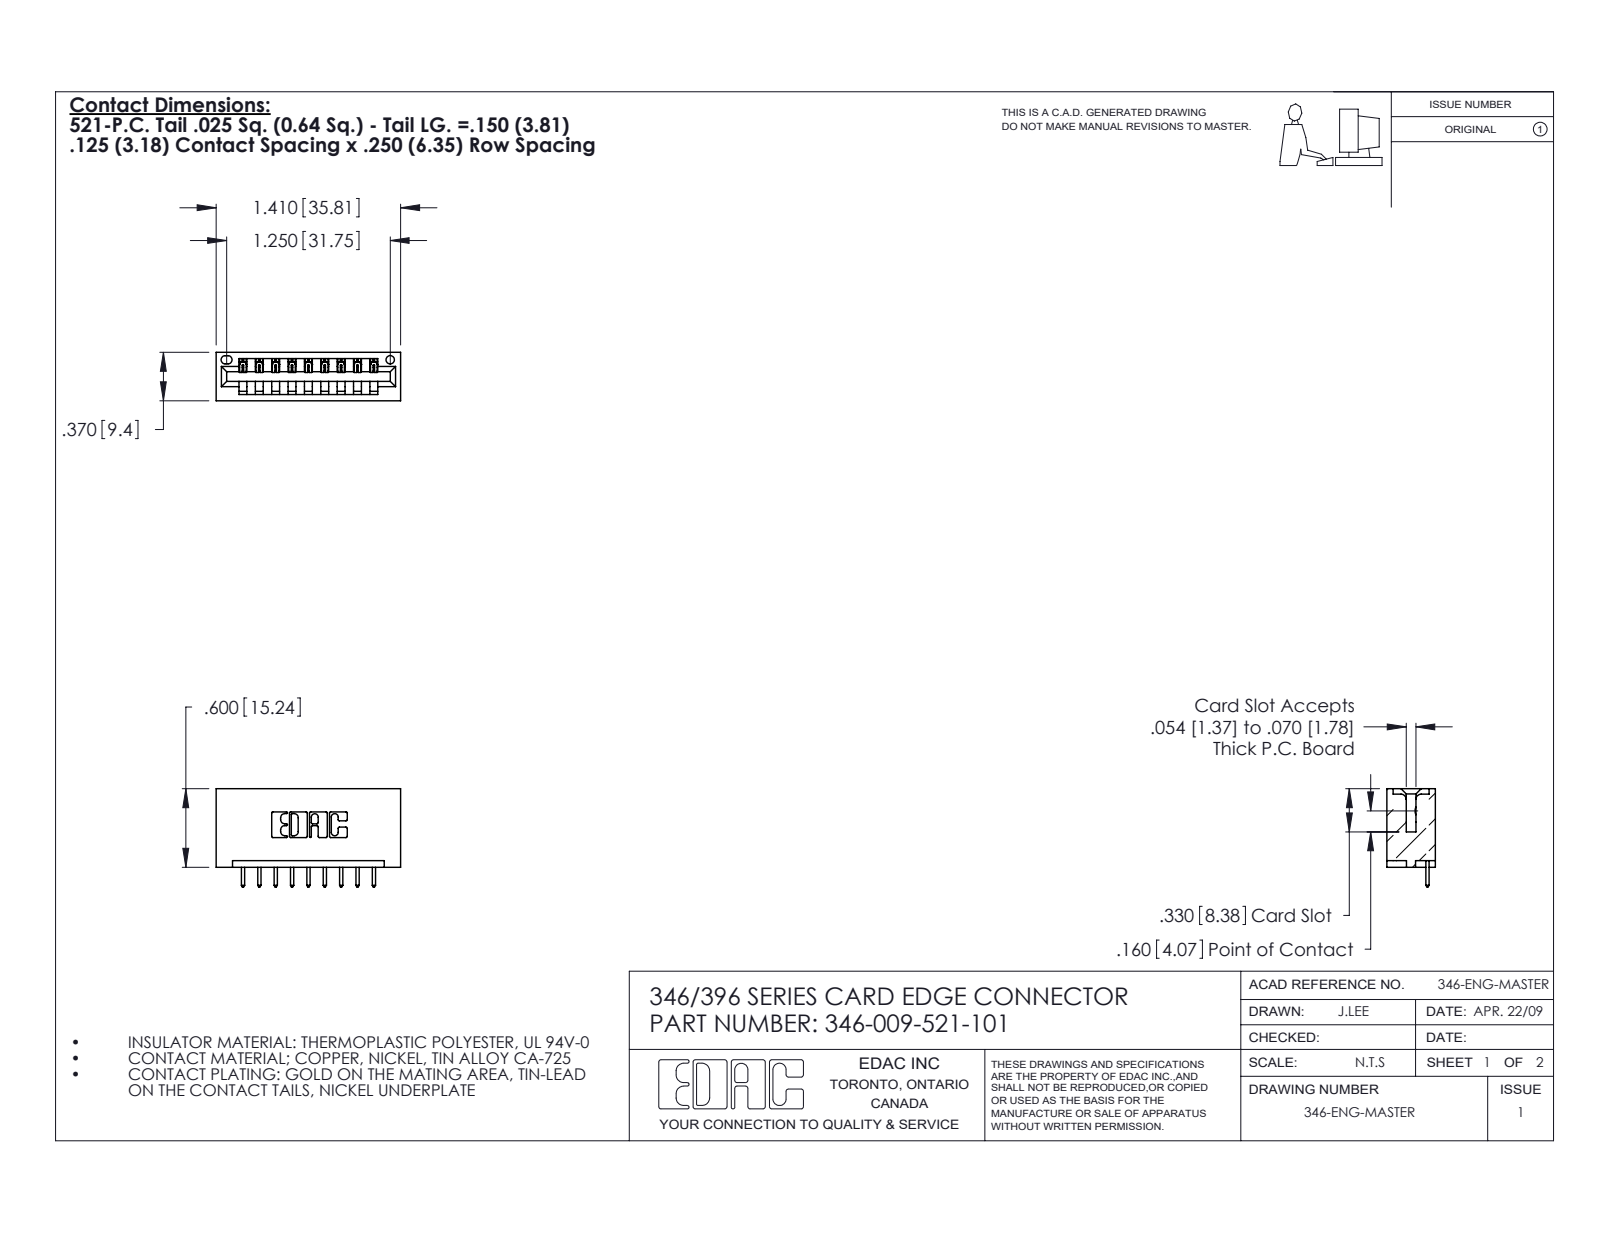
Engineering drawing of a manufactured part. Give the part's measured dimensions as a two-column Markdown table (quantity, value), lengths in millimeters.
| quantity | value |
| --- | --- |
| part name | 346-009-521-101; 345-292-001_345-293-121; 346 Part_No Mounting Lugs |
| STEP written by | SolidWorks 2020 (CONFIG_CONTROL_DESIGN) |
| units | millimeters |
| bodies | 10 solids, 636 faces (432 planar, 204 cylindrical, 0 other) |
| overall size | 35.8 × 19.1 × 9.4 |
| volume | 3 720 mm³ |
| surface area | 4 272 mm² |
| round holes (diameter × count) | 1.6 × 1 |
| partial cylindrical surfaces (radius × count) | 0.3 × 22, 0.2 × 18, 0.3 × 18, 0.2 × 6, 0.8 × 6, 0.7 × 3, 0.8 × 2, 1 × 2 |
| main face-to-face distances | 6.4, 1.2, 8.2, 9.4, 12.7, 3.2, 4.7, 1.7, 3.2, 3.8 |
